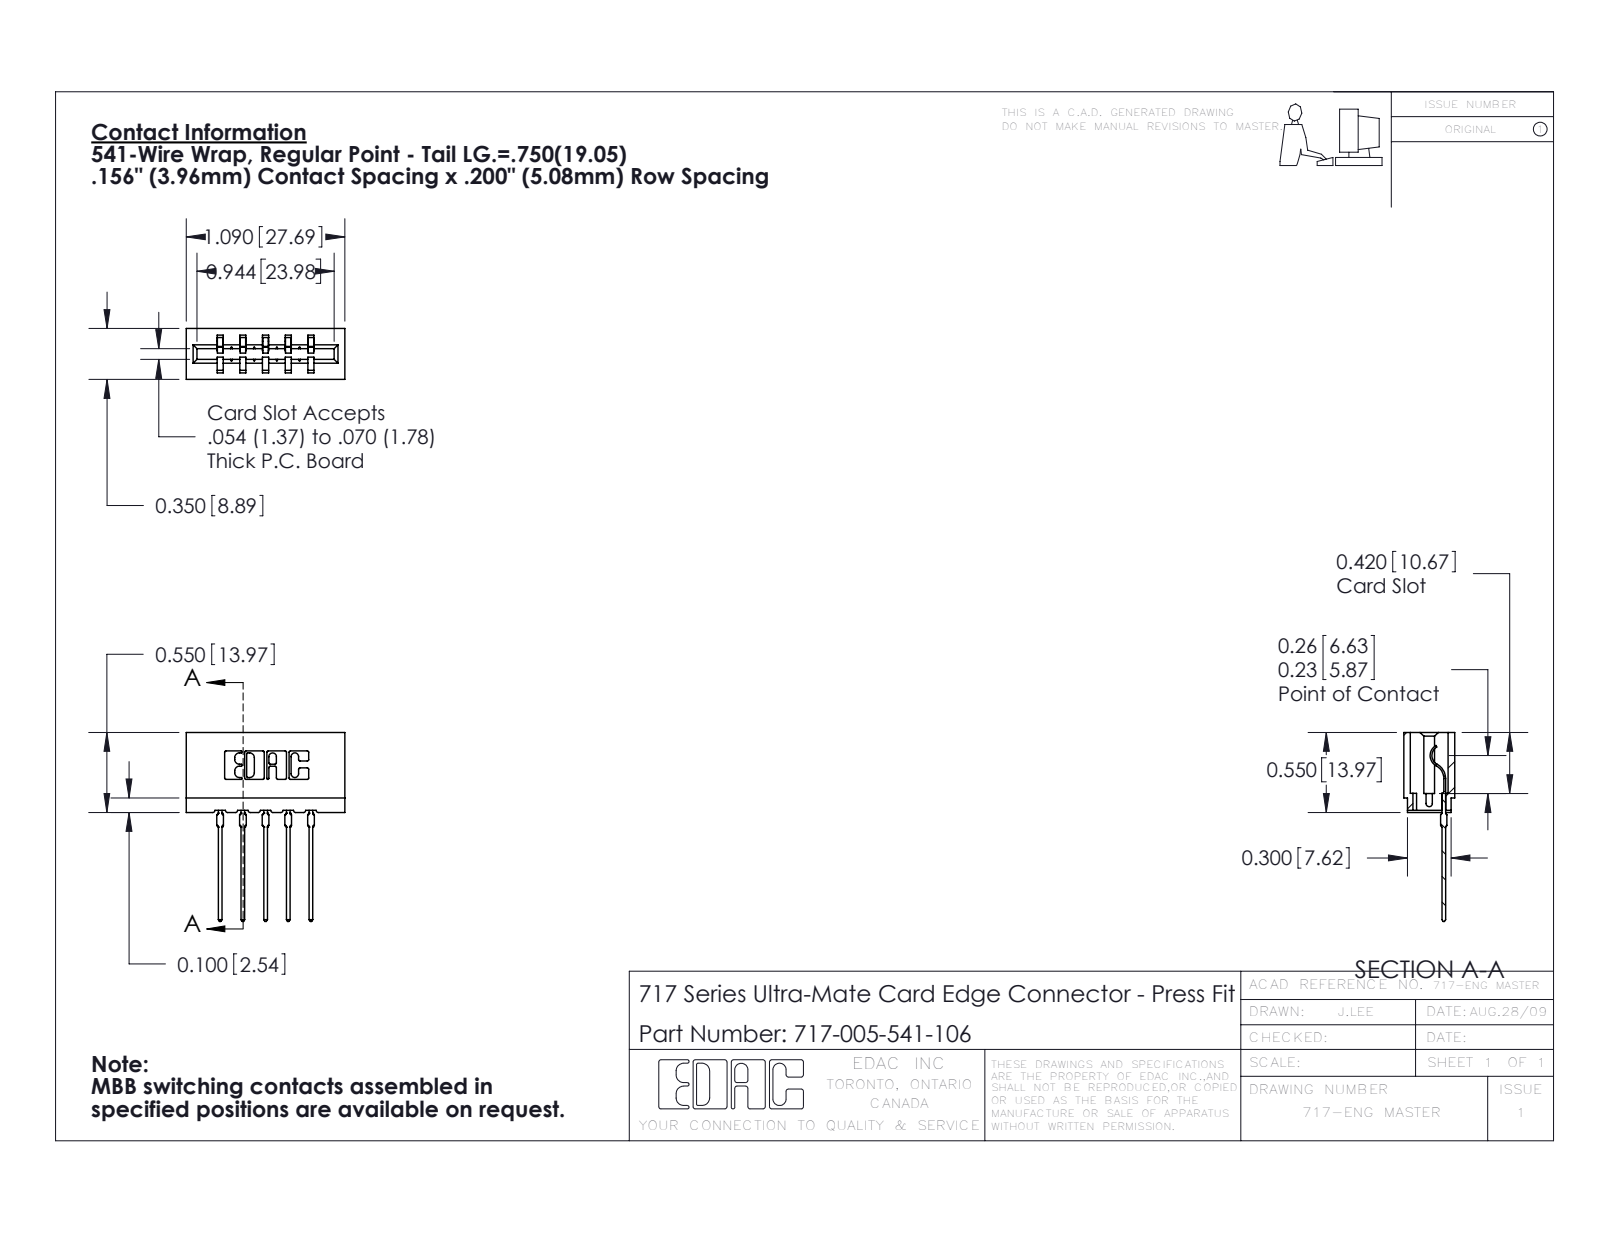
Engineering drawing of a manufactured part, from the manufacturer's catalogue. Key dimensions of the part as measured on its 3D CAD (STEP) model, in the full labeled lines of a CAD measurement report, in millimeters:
Part name (STEP PRODUCT): 745-292-001_541; 717 Part_Insulator Option - 06; 717-005-541-106
STEP written by: SolidWorks 2016 (CONFIG_CONTROL_DESIGN)
Units: millimetres
Bodies: 6 solids, 659 faces (394 planar, 135 cylindrical, 130 other)
Overall size (bounding box): 33 × 27.7 × 8.9
Volume: 2 520 mm³ · Surface area: 3 253 mm²
Partial cylindrical surfaces — rounded edges, fillets, slot ends (radius × count): R0.3 ×22, R0.4 ×10, R0.5 ×10, R0.2 ×6, R0.8 ×6, R0.1 ×4, R0.3 ×4, R0.7 ×3
Main face-to-face distances: 5.4, 4, 3.5, 8.9, 5, 1.1, 7.9, 7.9, 11.9, 1.9
